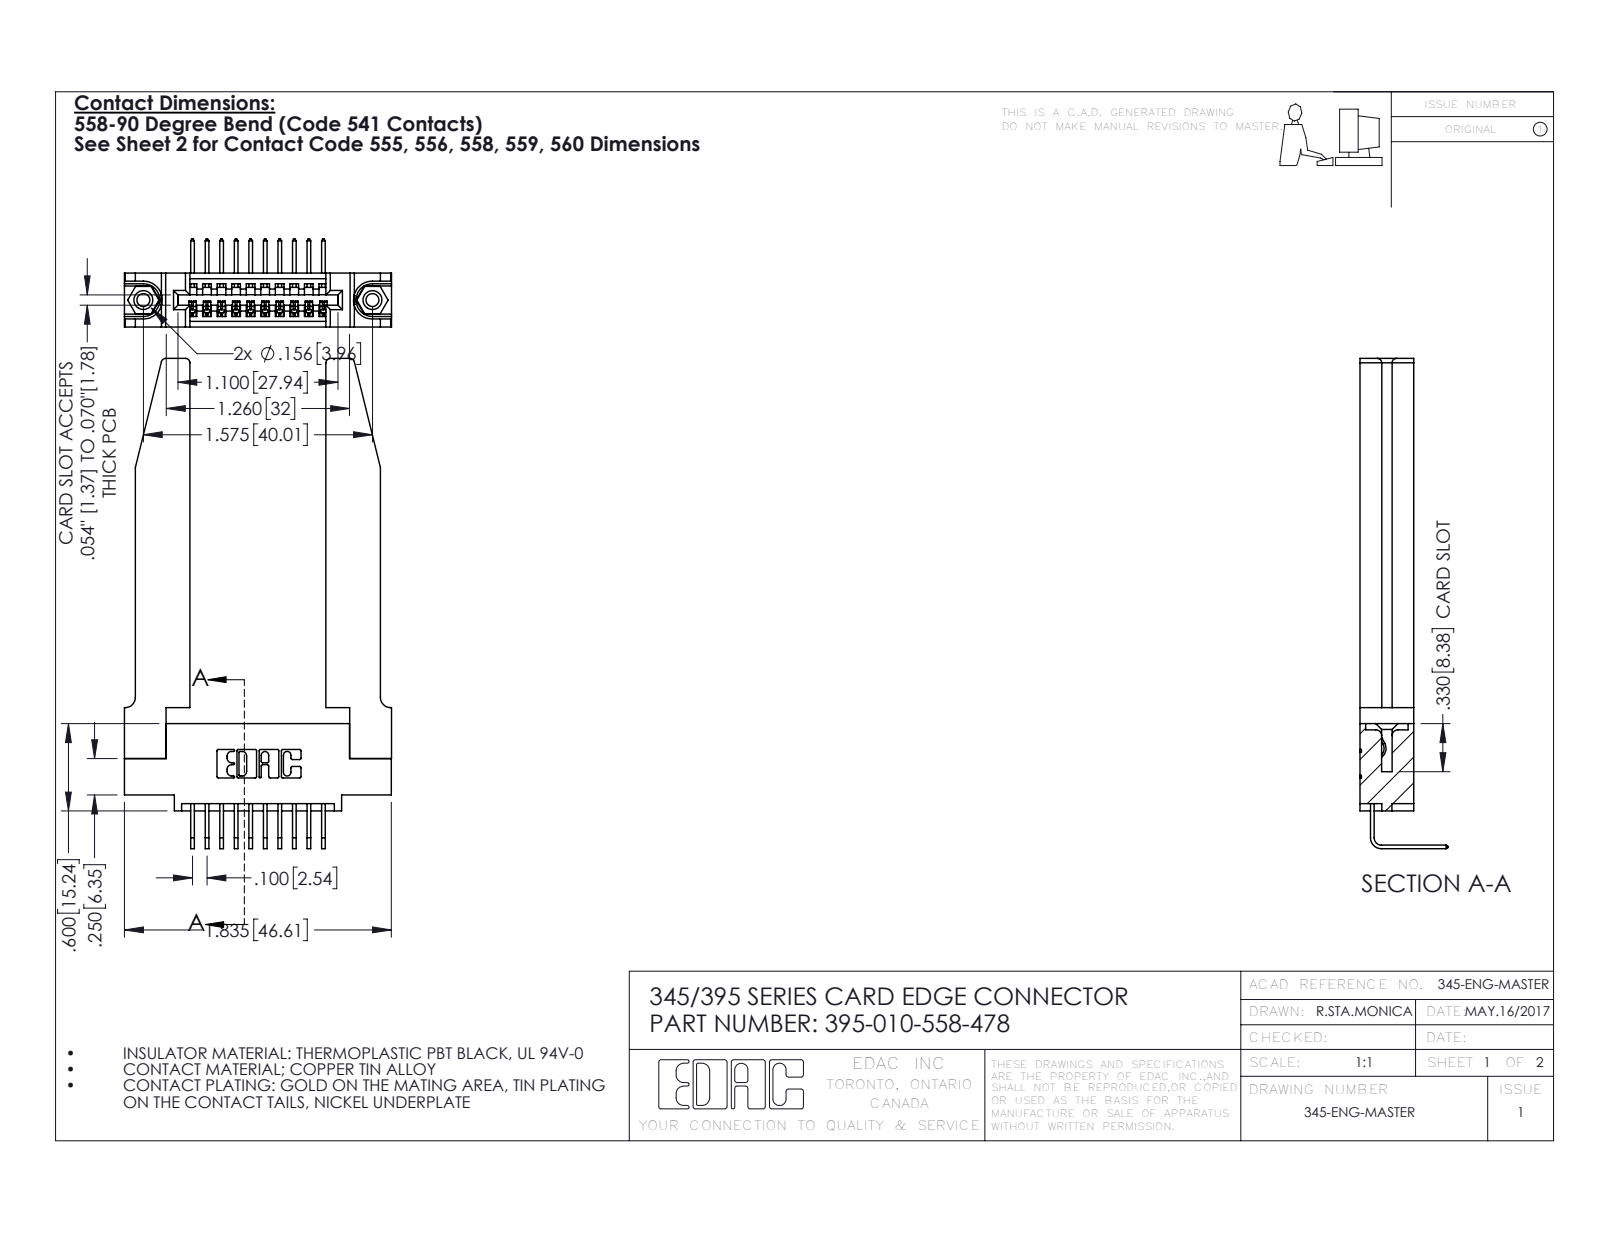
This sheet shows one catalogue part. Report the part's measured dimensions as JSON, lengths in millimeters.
{"part_name": "345-250-001_345-250-001-102; 345-220-078_345-220-078; 345-292-001_558 Tail - 2; 395-010-558-478 (+1 more)", "step_written_by": "SolidWorks 2016 (CONFIG_CONTROL_DESIGN)", "units": "millimeters", "bodies": {"solids": 15, "faces": 964, "planar": 646, "cylindrical": 266, "other": 52}, "overall_size": [85.6, 46.6, 15.4], "volume_mm3": 11900, "surface_area_mm2": 12170, "round_holes": [[2.3, 2], [3.2, 2], [4, 2], [1.6, 1]], "round_bosses_or_shafts": [[3.9, 2]], "partial_cylinders_radius": [[0.3, 22], [0.2, 20], [0.8, 8], [0.2, 6], [0.8, 6], [0.7, 3], [0.8, 2], [1, 2]], "face_to_face_distances": [9.4, 1.8, 7.6, 3.8, 3.8, 5.6, 2, 23.7, 5.1, 2.5], "hole_center_spacings": [6.9, 34.1, 40]}
